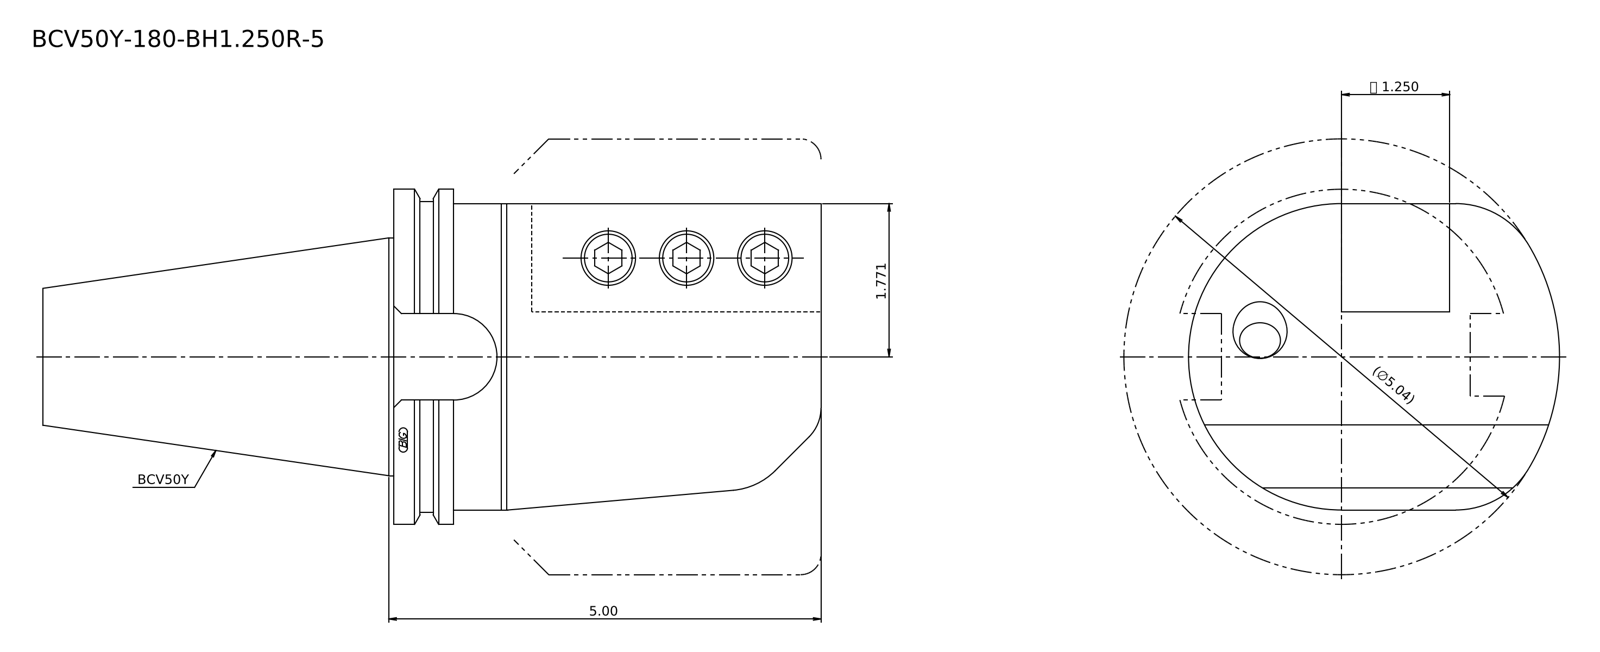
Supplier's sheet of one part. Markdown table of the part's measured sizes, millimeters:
| quantity | value |
| --- | --- |
| STEP written by | Kubotek KeyCreator 2011 V10.0.2 (22737) (automotive_design) |
| units | millimeters |
| bodies | 1 solid, 26 faces (14 planar, 8 cylindrical, 4 other) |
| overall size | 228.6 × 113.21 × 98.42 |
| volume | 1 126 000 mm³ |
| surface area | 79 168 mm² |
| round bosses / shafts (diameter × count) | 98.42 × 1, 91.29 × 1, 90 × 1, 69.85 × 1 |
| partial cylindrical surfaces (radius × count) | 25 × 2, 64 × 1 |
| main face-to-face distances | 125.5, 31.75, 228.6, 103.1, 107.95, 17.55, 120.65, 85, 22.95, 40.5 |
